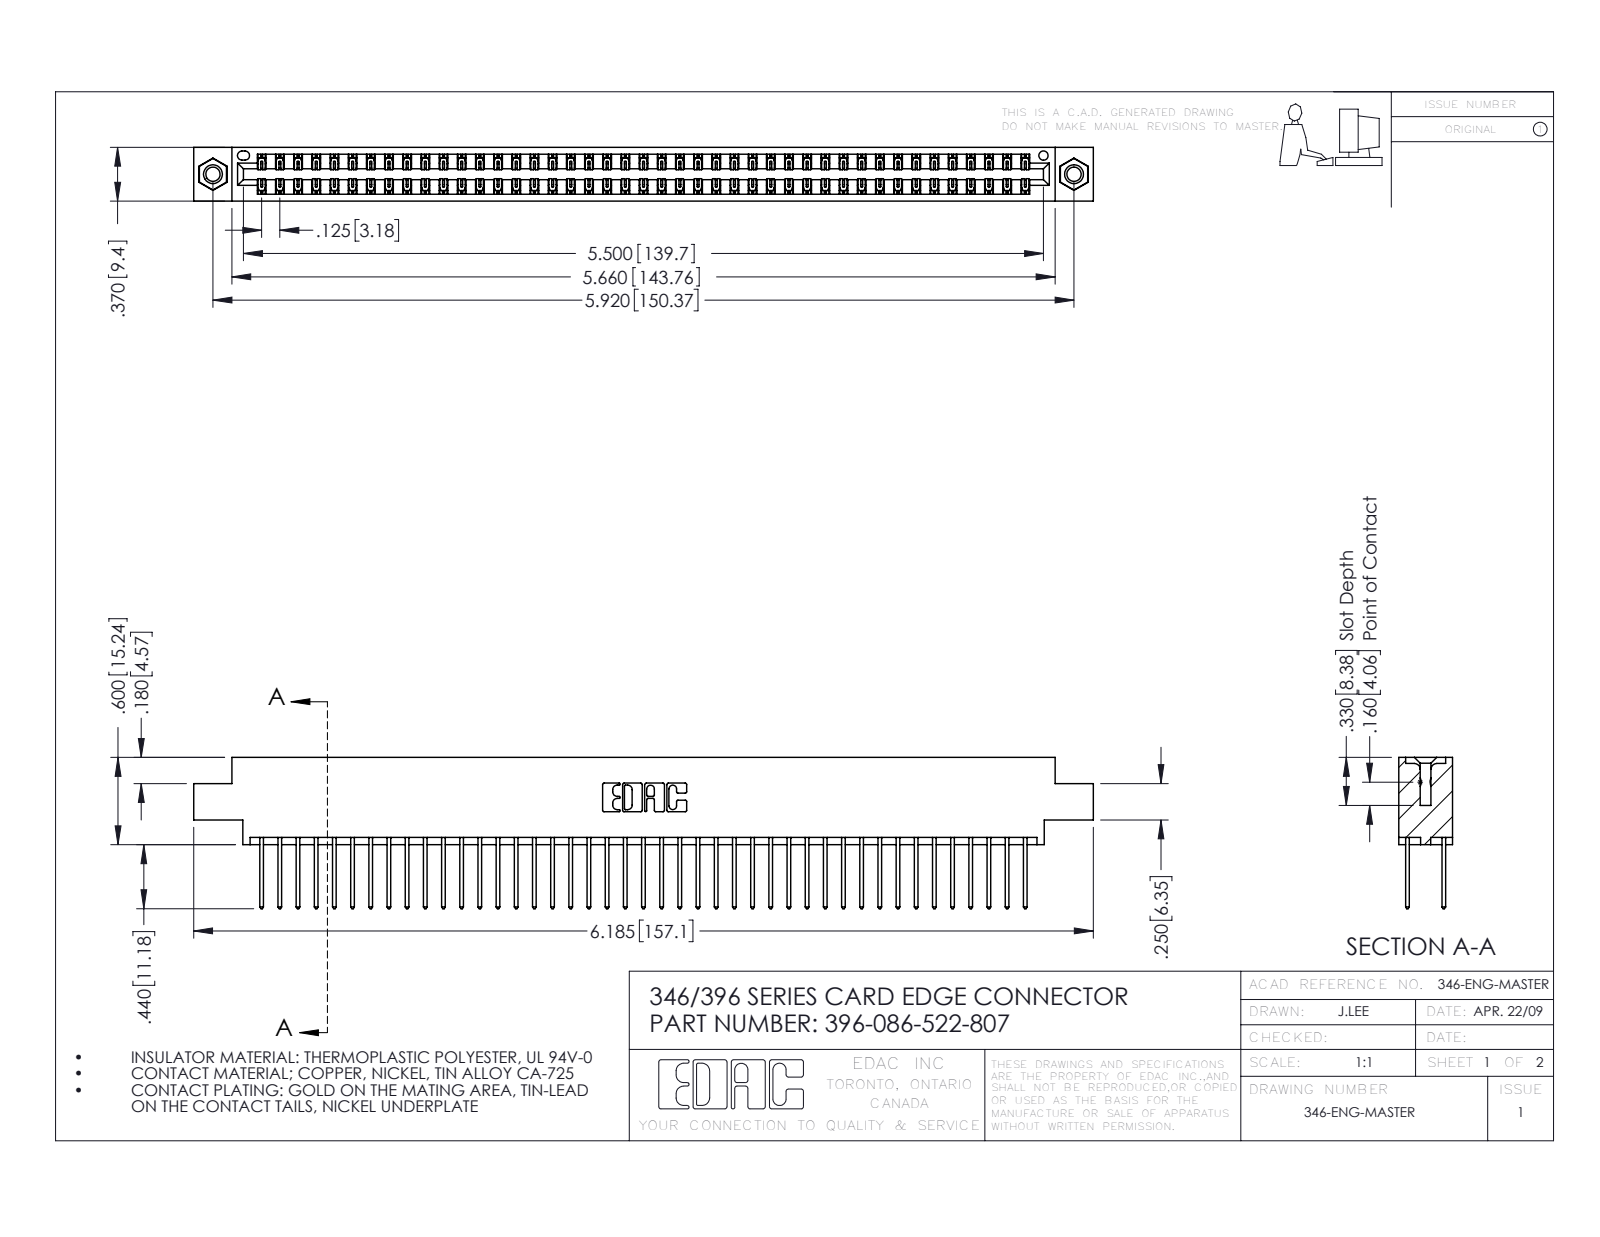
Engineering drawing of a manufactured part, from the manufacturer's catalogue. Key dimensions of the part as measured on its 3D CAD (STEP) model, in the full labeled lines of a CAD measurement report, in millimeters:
Part name (STEP PRODUCT): 345-292-001_345-293-122; 345-250-001_345-250-005-103; 346 Part_0.170 Offset - 0.156 Dia-TI; 396-086-522-807
STEP written by: SolidWorks 2016 (CONFIG_CONTROL_DESIGN)
Units: millimetres
Bodies: 89 solids, 4658 faces (3122 planar, 1520 cylindrical, 16 other)
Overall size (bounding box): 157.1 × 26.4 × 9.4
Volume: 15 400 mm³ · Surface area: 22 390 mm²
Round holes (diameter × count): ⌀2.5 ×2, ⌀3.2 ×2, ⌀4 ×2, ⌀1.6 ×1
Round bosses / shafts (diameter × count): ⌀3.9 ×2
Partial cylindrical surfaces — rounded edges, fillets, slot ends (radius × count): R0.2 ×129, R0.3 ×86, R0.3 ×22, R0.2 ×6, R0.8 ×6, R0.7 ×3, R0.4 ×2, R0.6 ×2
Main face-to-face distances: 1.2, 8.2, 6.4, 9.4, 1.8, 7.6, 0.6, 7, 5.6, 3.8
Hole centre spacings: 6.2, 145.1, 150.4
